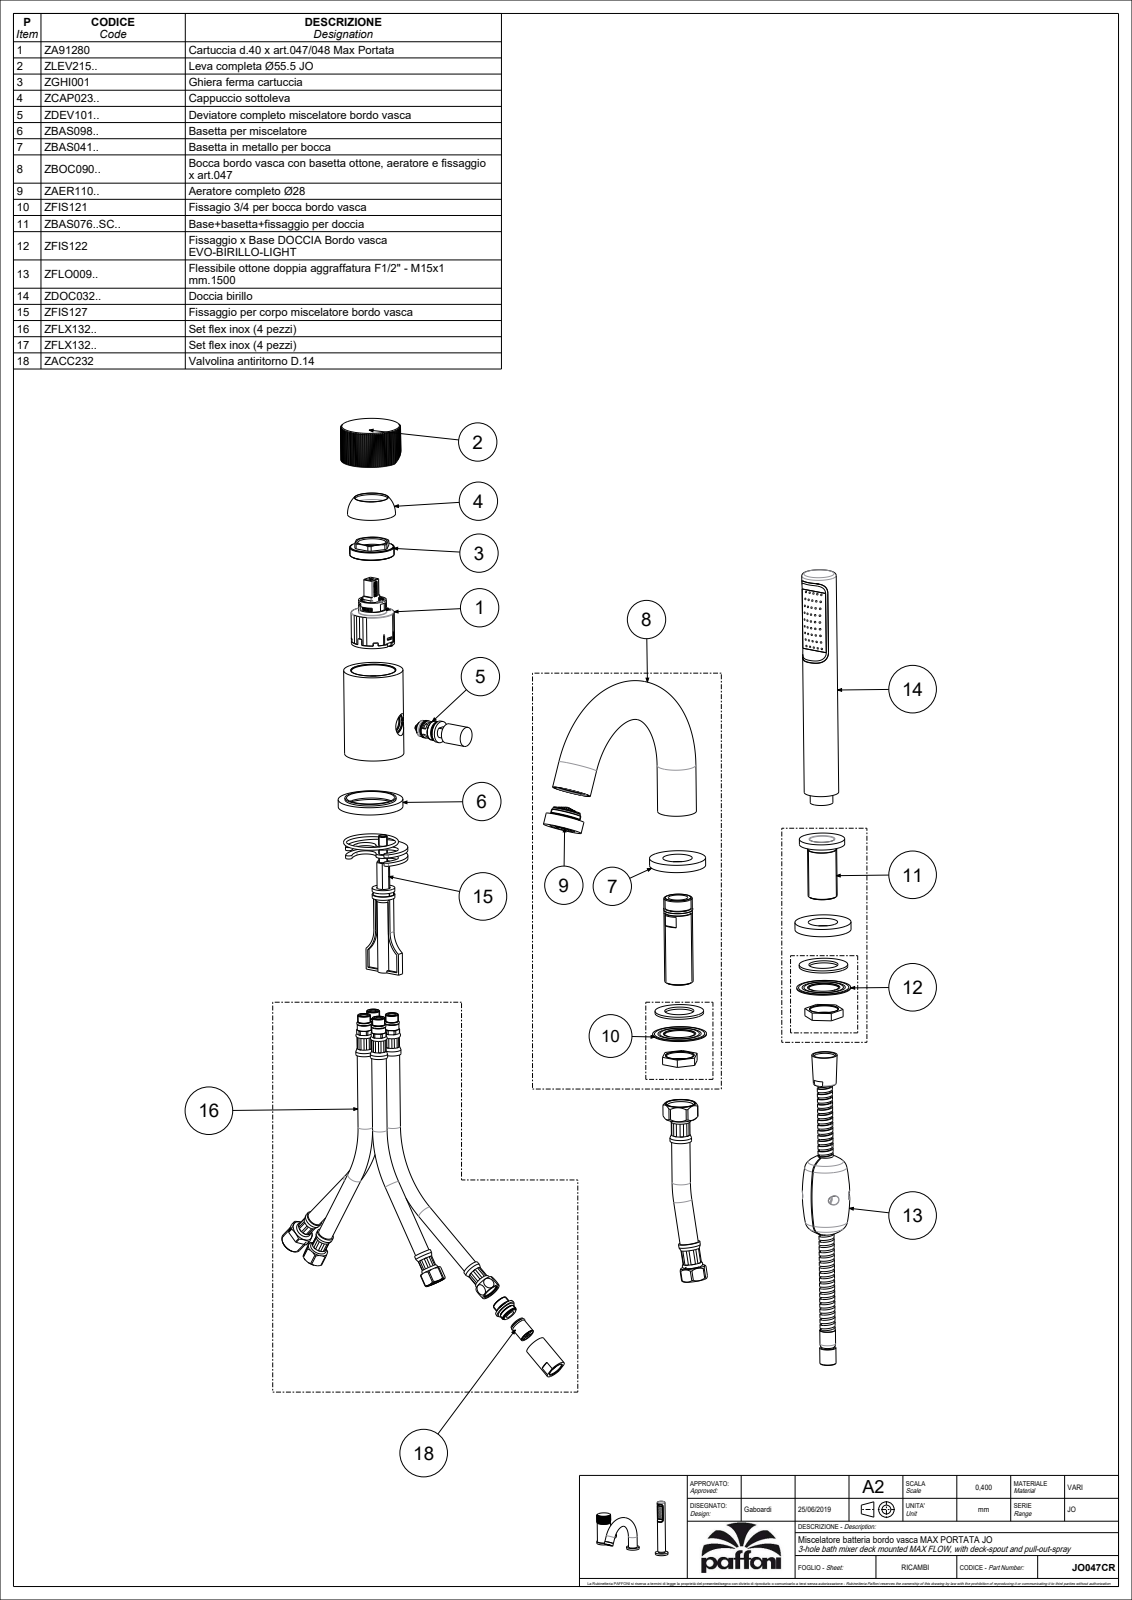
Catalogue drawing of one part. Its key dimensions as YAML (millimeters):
part_name: "JO047CR"
step_written_by: "CREO PARAMETRIC BY PTC INC, 2020044 (CONFIG_CONTROL_DESIGN)"
units: millimeters
bodies: {solids: 6, faces: 2704, planar: 1526, cylindrical: 794, other: 384}
overall_size: [356, 222, 209.82]
volume: 342396
surface_area: 210322
round_holes:
  - {diameter: 0.5, count: 61}
  - {diameter: 1.5, count: 45}
  - {diameter: 8, count: 5}
  - {diameter: 11, count: 4}
  - {diameter: 13, count: 4}
  - {diameter: 3.3, count: 2}
  - {diameter: 5, count: 2}
  - {diameter: 7, count: 2}
  - {diameter: 7.5, count: 2}
  - {diameter: 9.8, count: 2}
  - {diameter: 27.2, count: 2}
  - {diameter: 33, count: 2}
round_bosses_or_shafts:
  - {diameter: 52, count: 2}
  - {diameter: 44.2, count: 2}
  - {diameter: 36, count: 2}
  - {diameter: 33.9, count: 2}
  - {diameter: 12.8, count: 2}
  - {diameter: 10.5, count: 2}
  - {diameter: 10, count: 2}
  - {diameter: 5, count: 2}
partial_cylinders:
  - {radius: 0.25, count: 39}
  - {radius: 0.5, count: 21}
  - {radius: 0.15, count: 12}
  - {radius: 0.2, count: 12}
  - {radius: 1.5, count: 11}
  - {radius: 1.1, count: 10}
  - {radius: 2, count: 8}
  - {radius: 3, count: 8}
face_to_face_distances: [7, 2, 10, 119.3, 112.3, 1.5, 5, 12, 3, 9]
hole_center_spacings: [7.91, 13.76, 20.01, 6.5, 3.82, 5.73, 13, 26.39]
